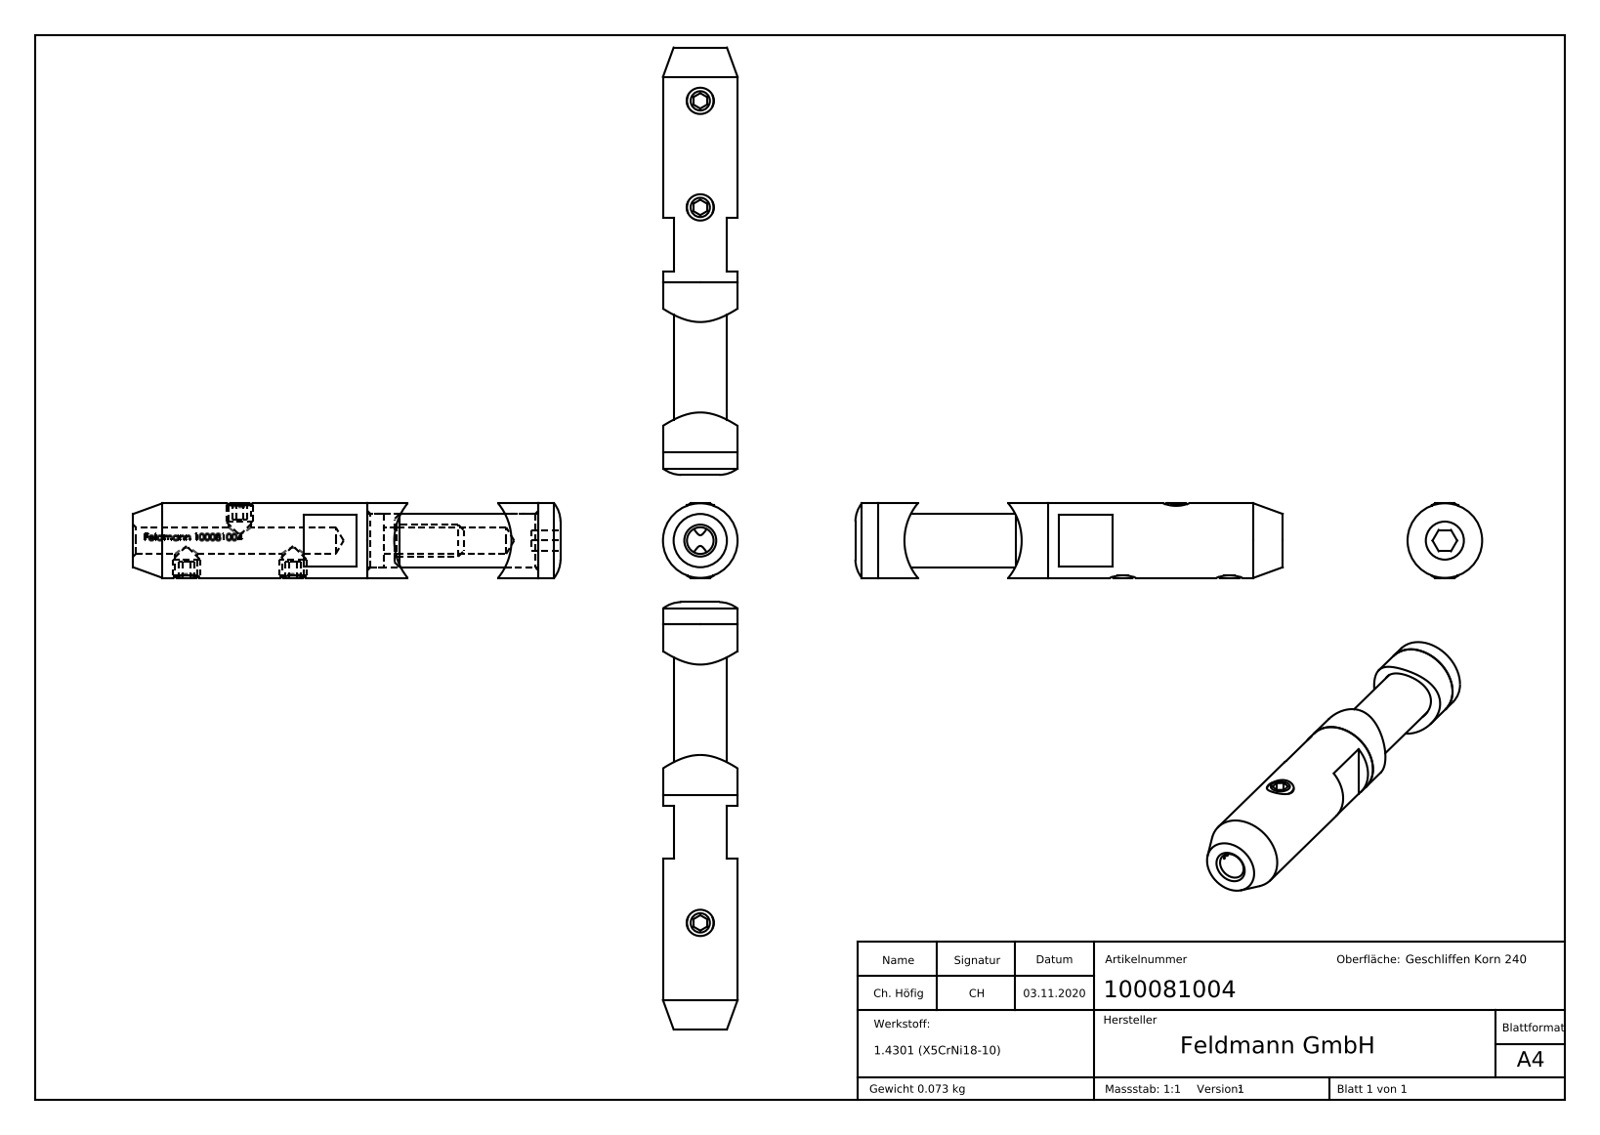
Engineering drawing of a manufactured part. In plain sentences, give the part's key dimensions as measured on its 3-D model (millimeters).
The part is named "10008100X Teil3; 10008100X Teil2; 10008100X Teil1; DIN 914 M5x6_DIN914 M5x6 (+5 more)". Its 3-D file was written by "SolidWorks 2018 (CONFIG_CONTROL_DESIGN)". It is 7 solids with 346 faces: 126 planar, 72 cylindrical and 148 other. Overall it measures 80.2 by 14 by 14 millimeters. Its volume is 9 225 cubic millimeters and its surface area 6 502 square millimeters. Round holes: 3 of diameter 4.2, 1 of diameter 5, 1 of diameter 10.1. Round bosses or shafts: 3 of diameter 5, 1 of diameter 14, 1 of diameter 10, 1 of diameter 6. Partial cylindrical surfaces (rounded edges, fillets, slot ends): 1 of radius 2.6, 1 of radius 11. The main face-to-face distances are 32, 10, 44, 3, 2, 5, 29, 76, 47, 2.5. The hole center spacings are 10, 20.
